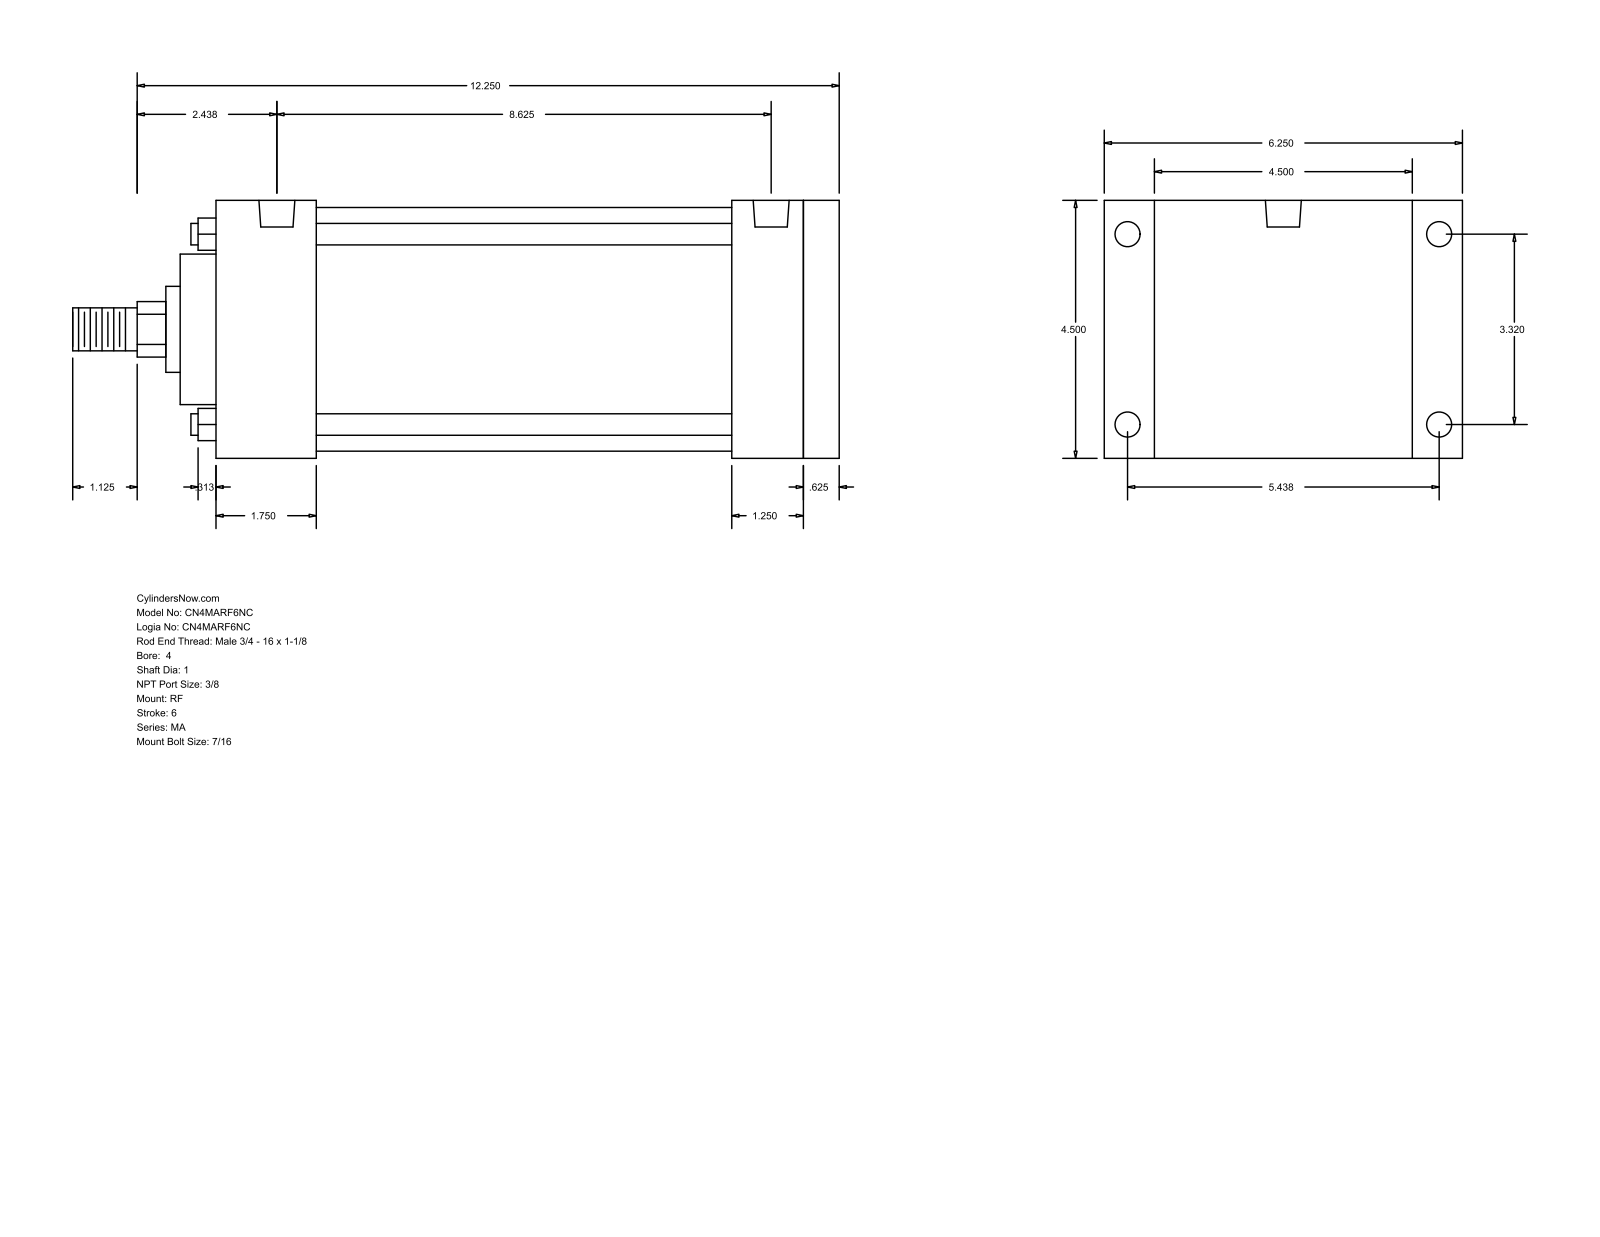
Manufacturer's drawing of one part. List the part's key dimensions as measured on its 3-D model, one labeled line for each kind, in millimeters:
Part name (STEP PRODUCT): MA_RF__0400_1
STEP written by: GSSL Pune (CONFIG_CONTROL_DESIGN)
Units: millimetres
Bodies: 0 solids, 94 faces (65 planar, 29 cylindrical, 0 other)
Overall size (bounding box): 339.73 × 158.75 × 114.3
Round holes (diameter × count): ⌀11.11 ×8, ⌀15.93 ×2
Round bosses / shafts (diameter × count): ⌀9.53 ×4, ⌀107.95 ×1, ⌀66.67 ×1, ⌀38.1 ×1, ⌀25.4 ×1, ⌀19.05 ×1
Partial cylindrical surfaces — rounded edges, fillets, slot ends (radius × count): R12.29 ×1
Main face-to-face distances: 114.3, 276.23, 260.35, 15.88, 22.23, 136.53, 228.6, 31.75, 47.63, 44.46
Hole centre spacings: 4.76, 84.32, 138.12, 161.82, 209.56, 214.32, 219.08
